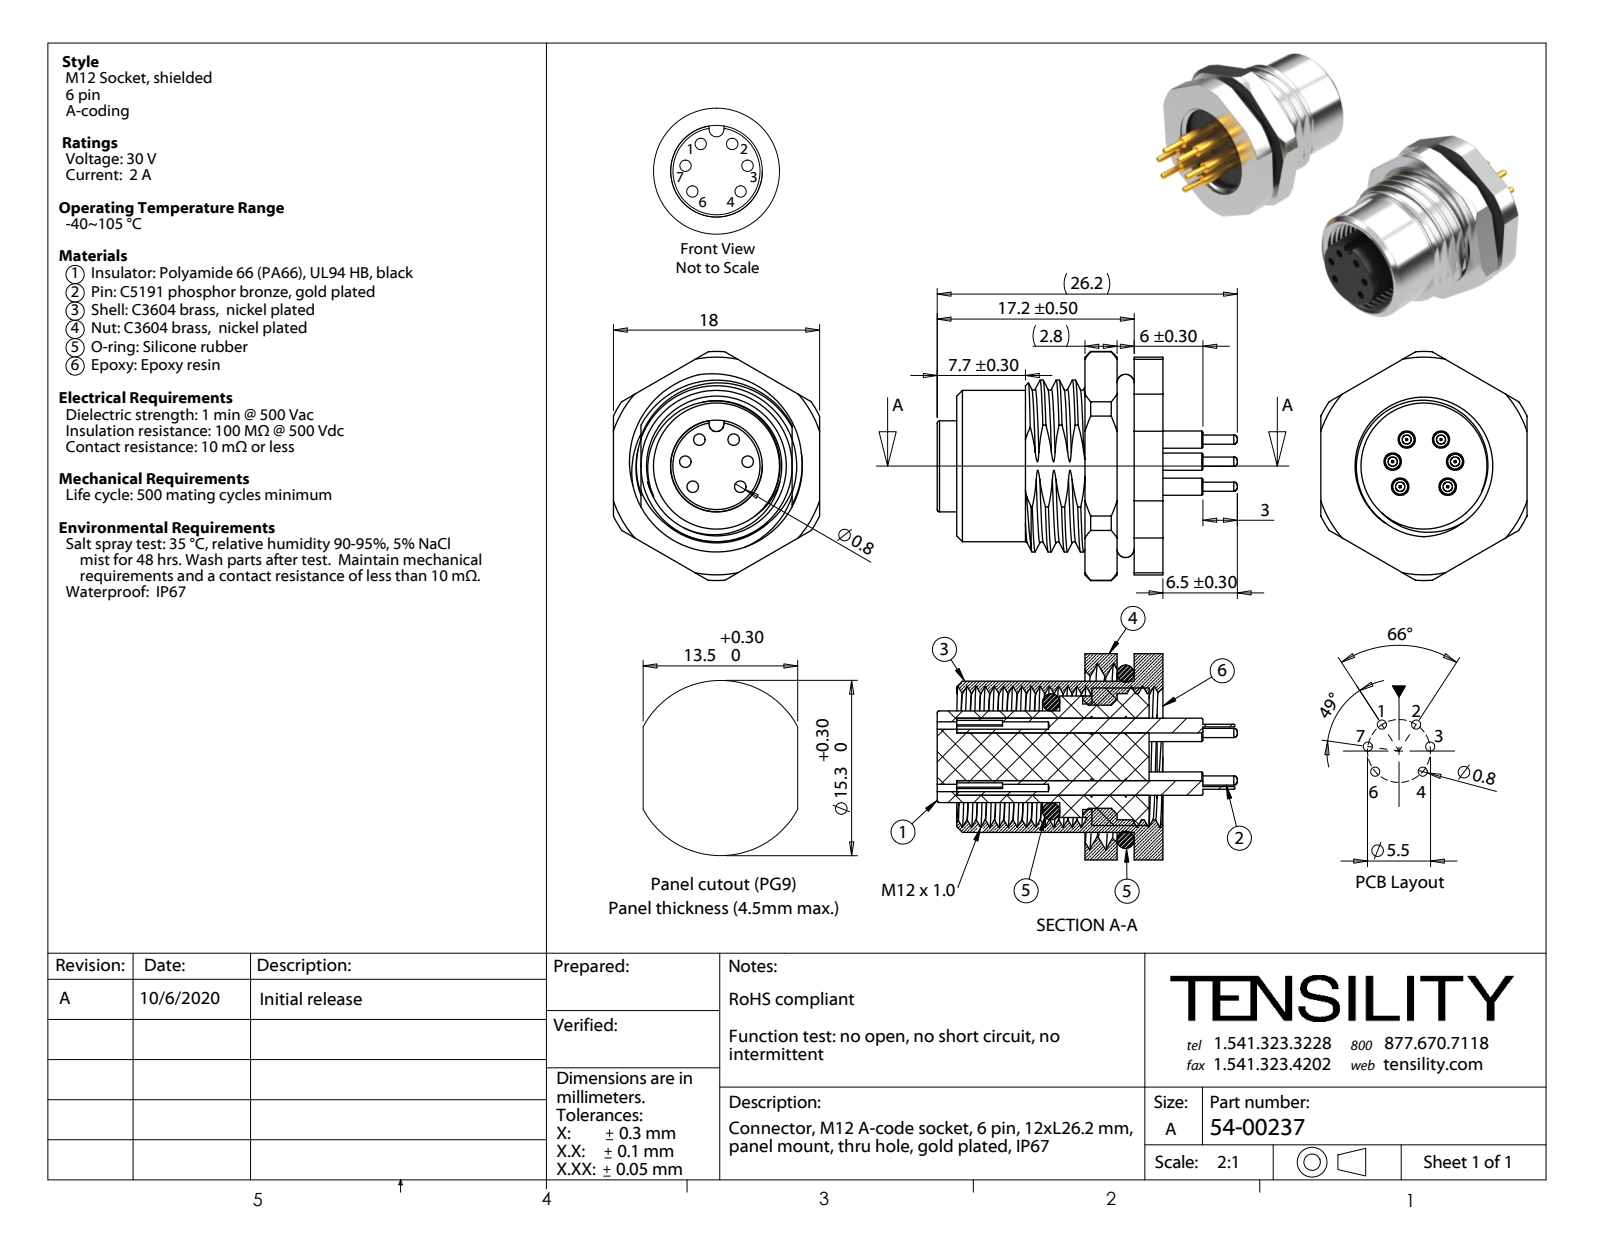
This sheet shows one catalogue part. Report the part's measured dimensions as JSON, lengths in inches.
{"part_name": "54-00237-02; 54-00237-05; 54-00237-01; 54-00237-03 (+3 more)", "step_written_by": "SolidWorks 2021 (CONFIG_CONTROL_DESIGN)", "units": "inches", "bodies": {"solids": 11, "faces": 430, "planar": 113, "cylindrical": 167, "other": 150}, "overall_size": [1.031, 0.787, 0.709], "volume_in3": 0.175, "surface_area_in2": 8.775, "round_holes": [[0.039, 6], [0.354, 1], [0.433, 1], [0.551, 1]], "round_bosses_or_shafts": [[0.059, 6], [0.031, 6], [0.52, 1], [0.472, 1], [0.417, 1], [0.362, 1], [0.315, 1]], "partial_cylinders_radius": [[0.026, 1], [0.295, 1], [0.374, 1], [0.394, 1]], "face_to_face_distances": [0.11, 0.098, 0.709, 0.059, 0.051, 0.157, 0.047, 0.197, 0.087, 0.268], "hole_center_spacings": [0.108, 0.089, 0.09, 0.163, 0.183, 0.207, 0.215, 0.118]}
